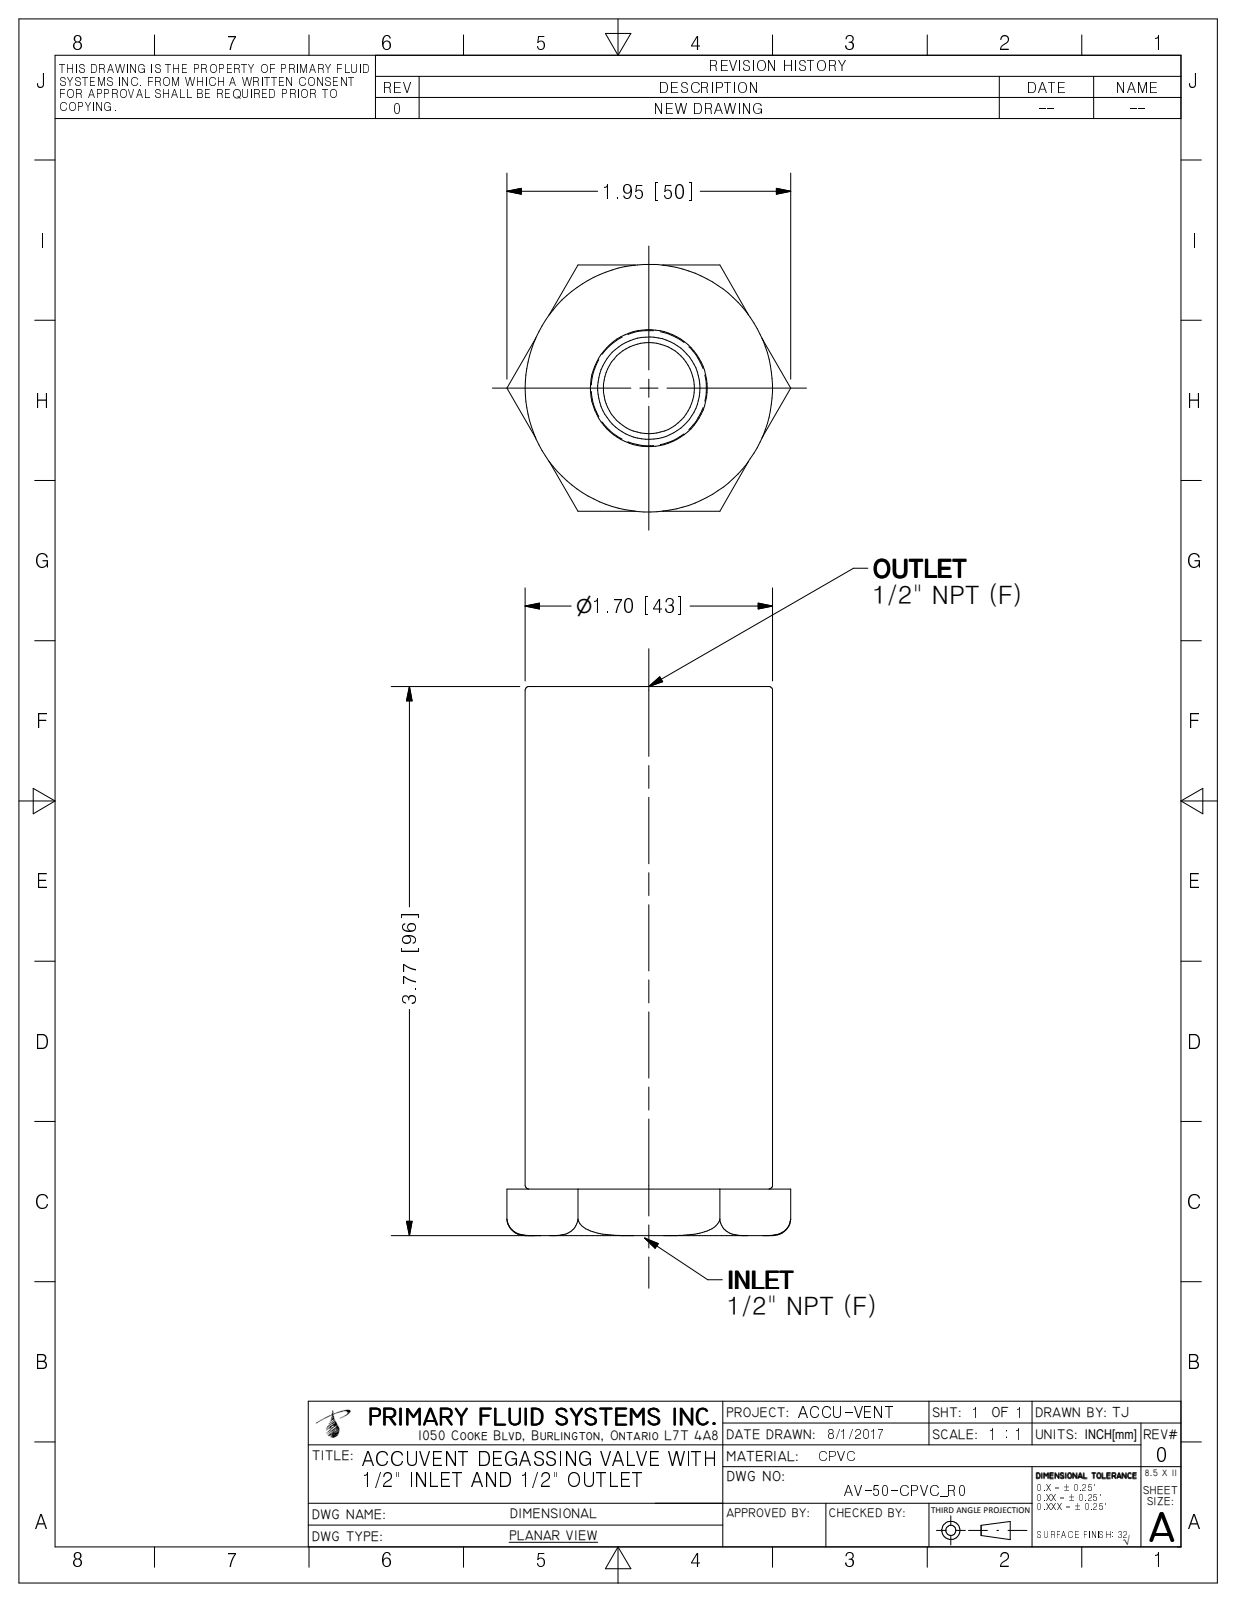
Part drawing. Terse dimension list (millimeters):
name: AV-50-CPVC_R0
written by: Autodesk Inventor 2009 (AUTOMOTIVE_DESIGN)
unit: mm
bodies: 1 solid, 23 faces (11 planar, 3 cylindrical, 9 other)
size: 95.8 × 49.6 × 43.2
volume: 130 600 mm³; area: 18 460 mm²
holes: 1× ⌀17.9, 1× ⌀21.3
bosses: 1× ⌀43.2
face distances: 95.8, 42.9, 17, 78.7, 77.6, 60.6, 18.2, 8.1, 8.9, 69.5
